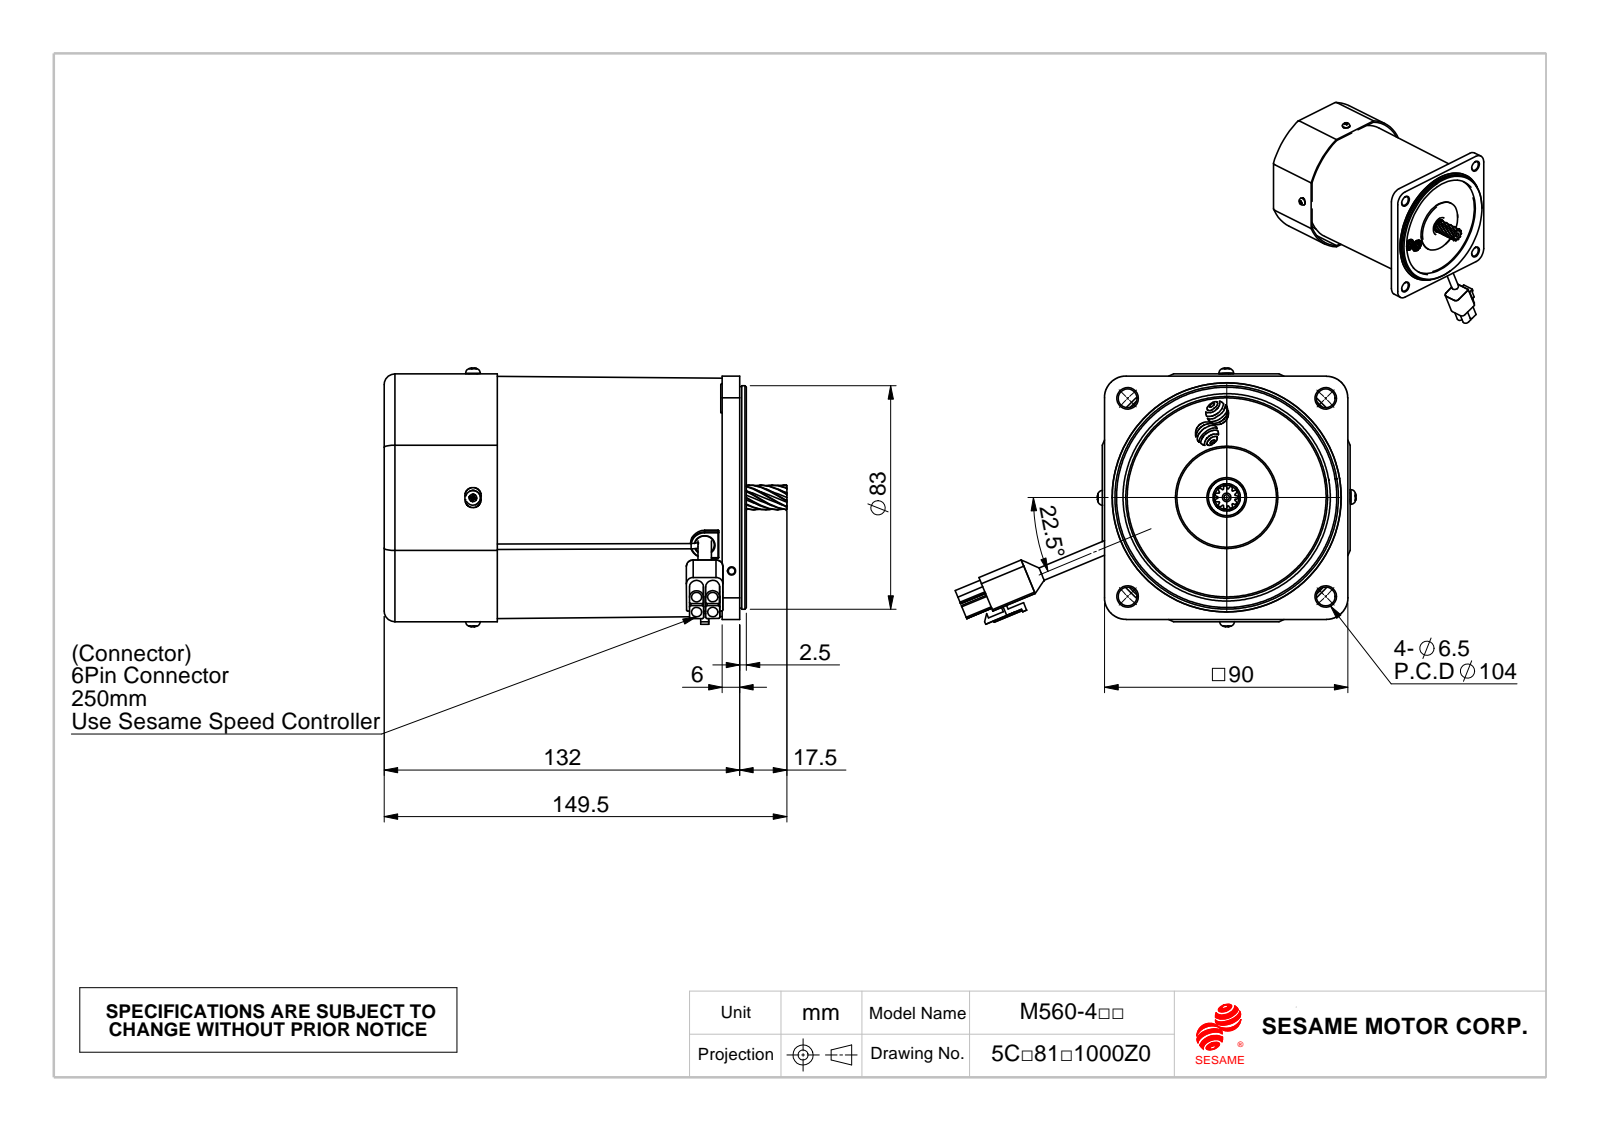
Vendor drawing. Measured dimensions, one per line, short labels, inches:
name: M560-R-F; 線扣; 風扇蓋FC-9042-33; 油封10x26x5 (+2 more)
written by: SolidWorks 2010 (CONFIG_CONTROL_DESIGN)
unit: in
bodies: 13 solids, 907 faces (296 planar, 429 cylindrical, 182 other)
size: 5.886 × 5.856 × 3.775
volume: 45.21 in³; area: 182.9 in²
holes: 7× ⌀0.098, 4× ⌀0.15, 4× ⌀0.217, 4× ⌀0.276, 2× ⌀0.079, 2× ⌀0.122, 2× ⌀0.945, 1× ⌀0.256, 1× ⌀0.283, 1× ⌀0.374, 1× ⌀0.539, 1× ⌀0.591
bosses: 4× ⌀0.217, 4× ⌀0.118, 2× ⌀1.85, 2× ⌀0.079, 1× ⌀3.316, 1× ⌀3.268, 1× ⌀3.236, 1× ⌀2.283
rounds: 16× R0.012, 14× R0.02, 14× R0.039, 8× R0.01, 8× R0.031, 8× R0.059, 8× R0.065, 8× R0.115
face distances: 0.039, 1.063, 3.583, 0.287, 5.094, 5.134, 1.102, 4.031, 4.846, 4.807
hole spacings: 0.236, 2.047, 0.167, 0.197, 0.142, 1.503, 2.881, 2.895
